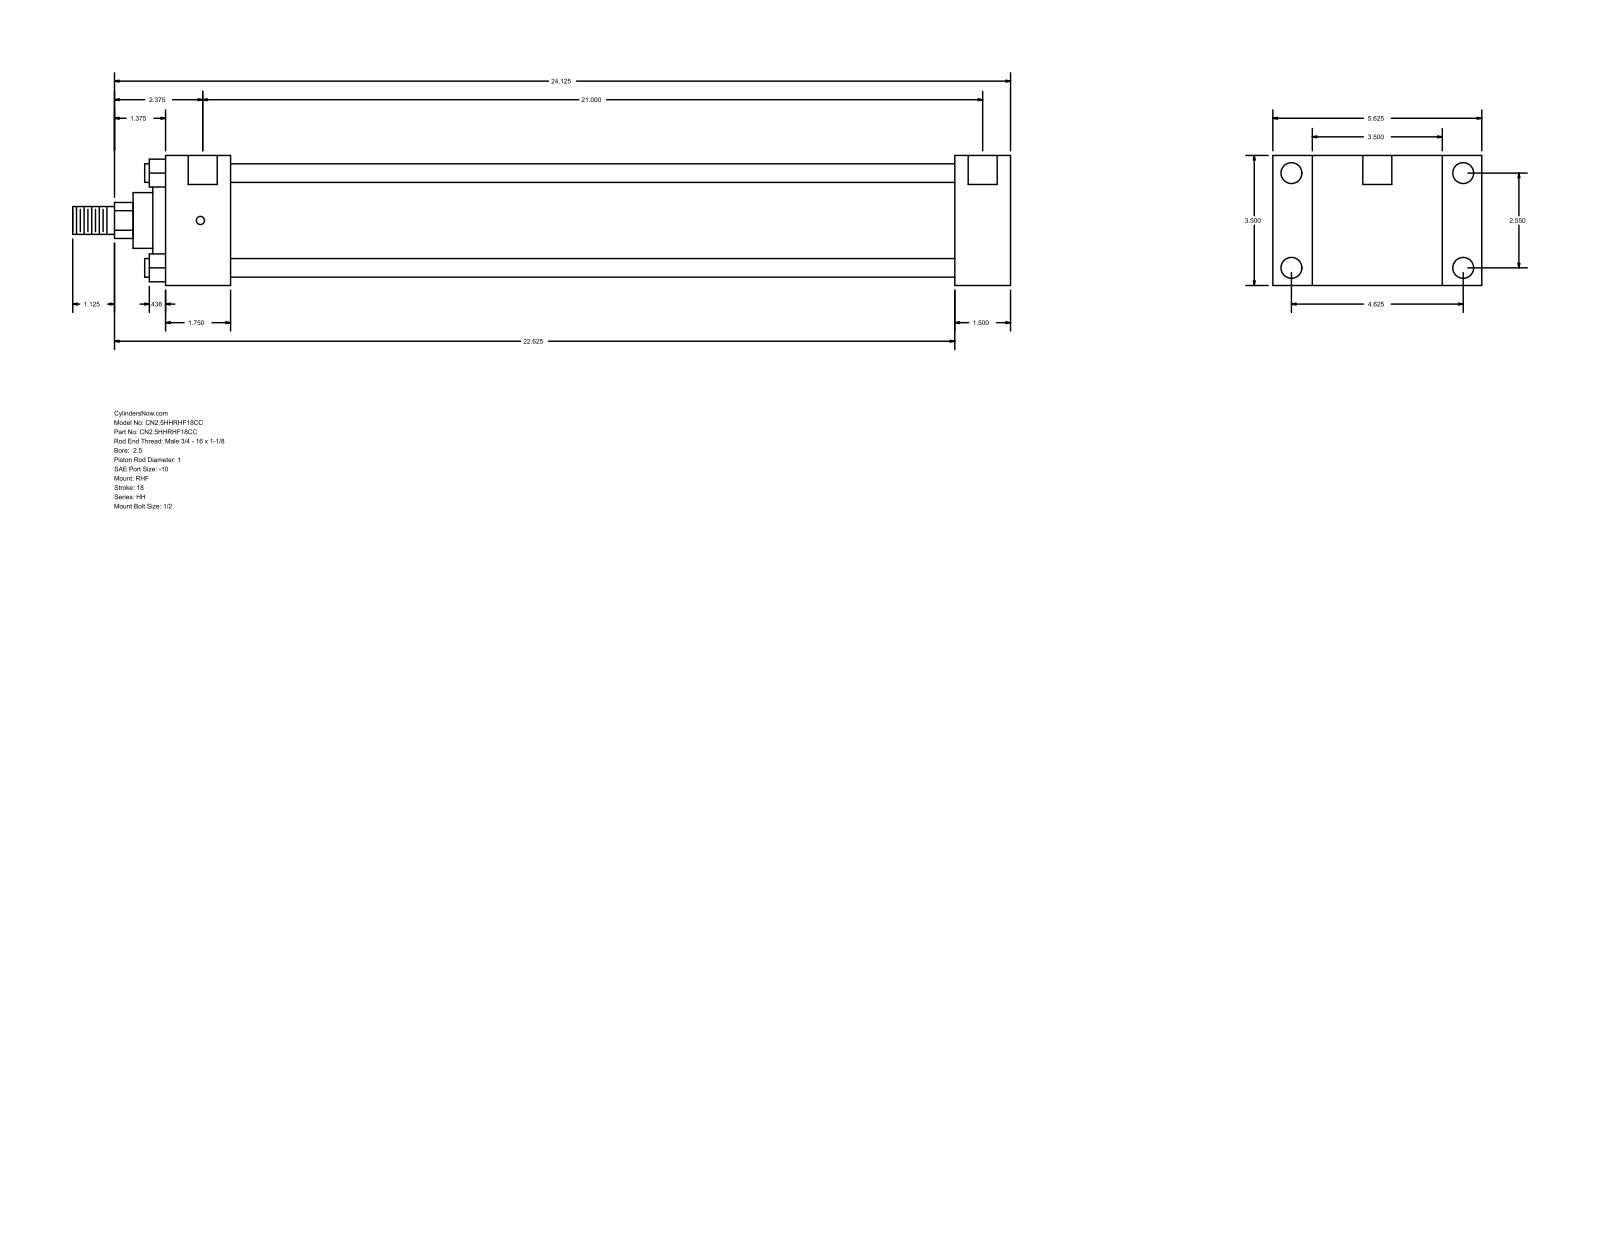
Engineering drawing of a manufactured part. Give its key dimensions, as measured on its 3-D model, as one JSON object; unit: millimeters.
{"part_name": "HH_RHF__0250_1", "step_written_by": "GSSL Pune (CONFIG_CONTROL_DESIGN)", "units": "millimeters", "bodies": {"solids": 0, "faces": 90, "planar": 61, "cylindrical": 29, "other": 0}, "overall_size": [641.35, 142.88, 88.9], "round_holes": [[5.56, 4], [14.3, 4], [19.84, 2]], "round_bosses_or_shafts": [[12.7, 4], [73.03, 1], [60.33, 1], [38.1, 1], [25.4, 1], [19.05, 1]], "partial_cylinders_radius": [[12.29, 1]], "face_to_face_distances": [88.9, 38.1, 26.99, 115.89, 539.75, 577.85, 142.88, 44.46, 495.29, 533.39], "hole_center_spacings": [64.76, 117.48, 134.15, 536.57, 1.58, 1.59, 533.4, 534.98]}
